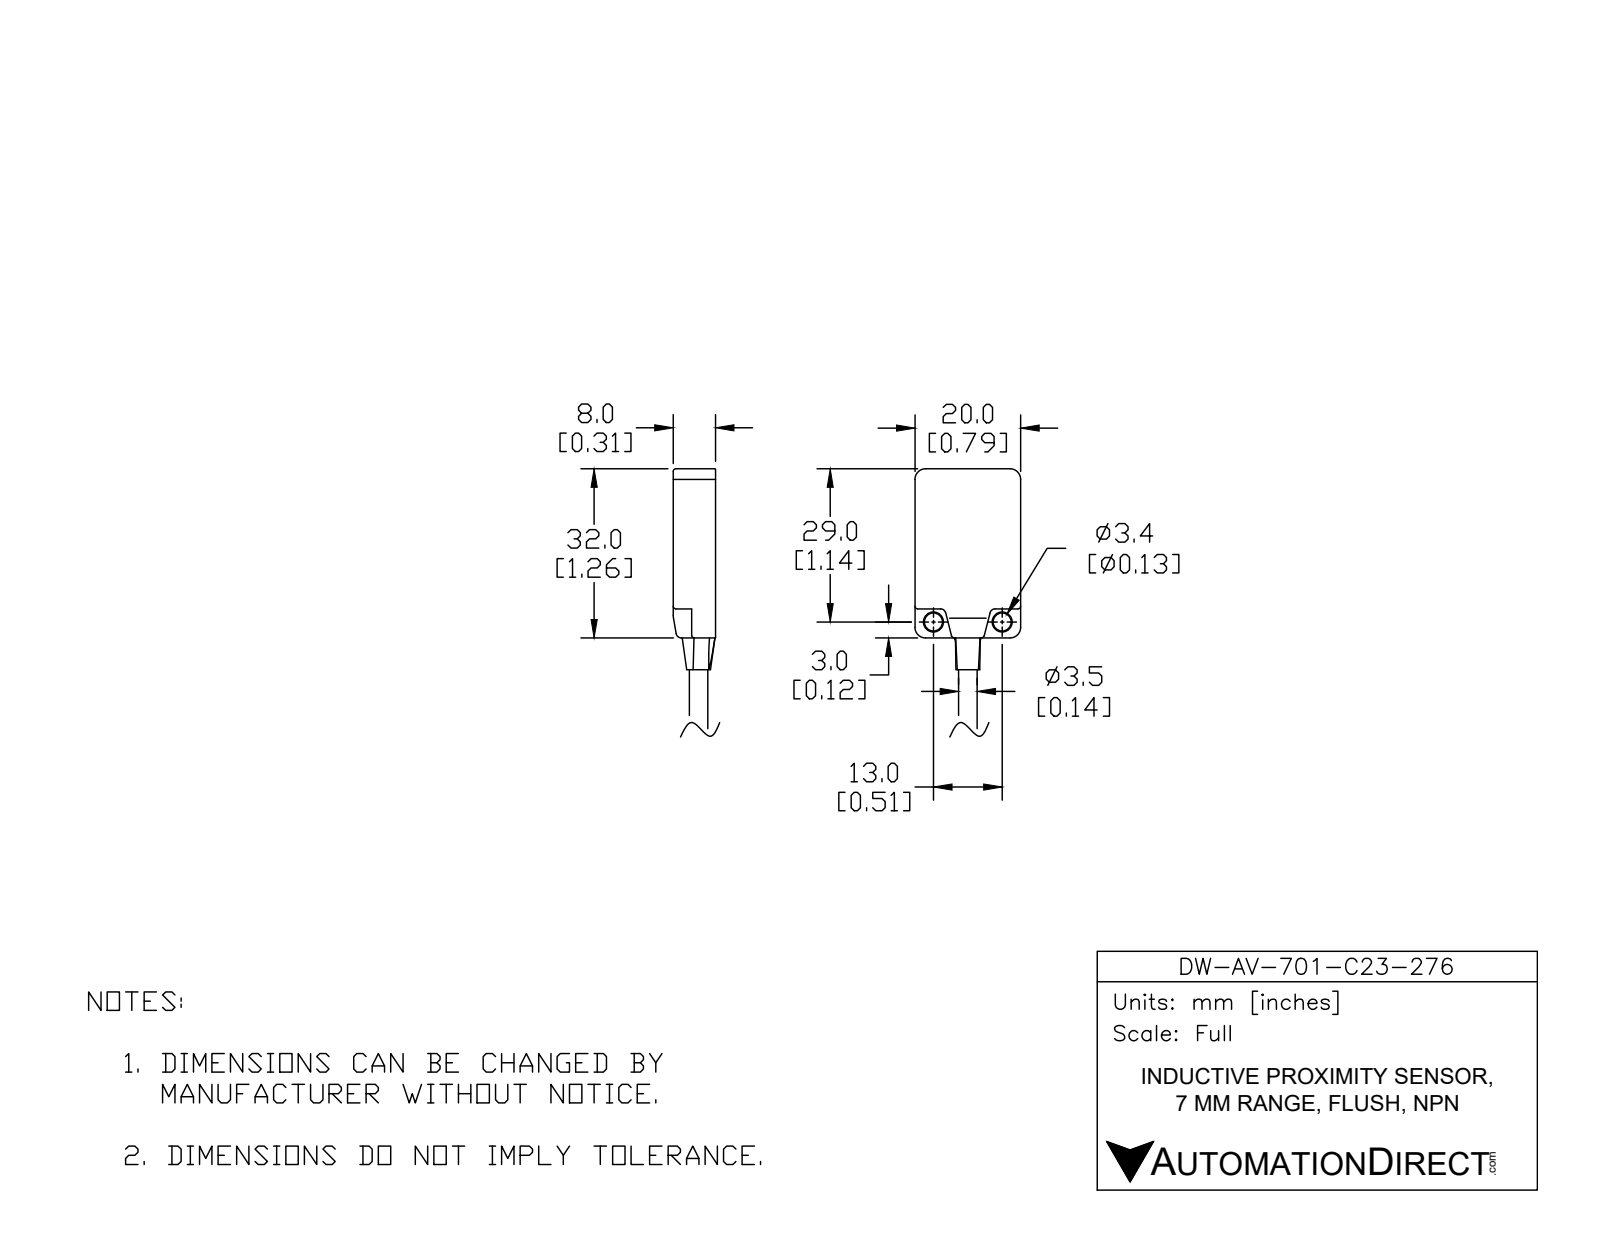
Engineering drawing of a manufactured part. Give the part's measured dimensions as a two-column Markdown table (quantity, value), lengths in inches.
| quantity | value |
| --- | --- |
| part name | DW-AV-701-C23-276 |
| STEP written by | SolidWorks 2017 (AUTOMOTIVE_DESIGN) |
| units | inches |
| bodies | 1 solid, 97 faces (37 planar, 36 cylindrical, 24 other) |
| overall size | 5.237 × 0.787 × 0.315 |
| volume | 0.344 in³ |
| surface area | 4.965 in² |
| round holes (diameter × count) | 0.134 × 2 |
| round bosses / shafts (diameter × count) | 0.039 × 3, 0.13 × 1 |
| partial cylindrical surfaces (radius × count) | 0.02 × 10, 0.039 × 6, 0.02 × 4, 0.022 × 4, 0.079 × 4 |
| main face-to-face distances | 0.315, 0.787, 1.26, 0.177, 0.138, 1.043, 0.217, 0.037, 0.039, 0.713 |
| hole center spacings | 0.512 |
